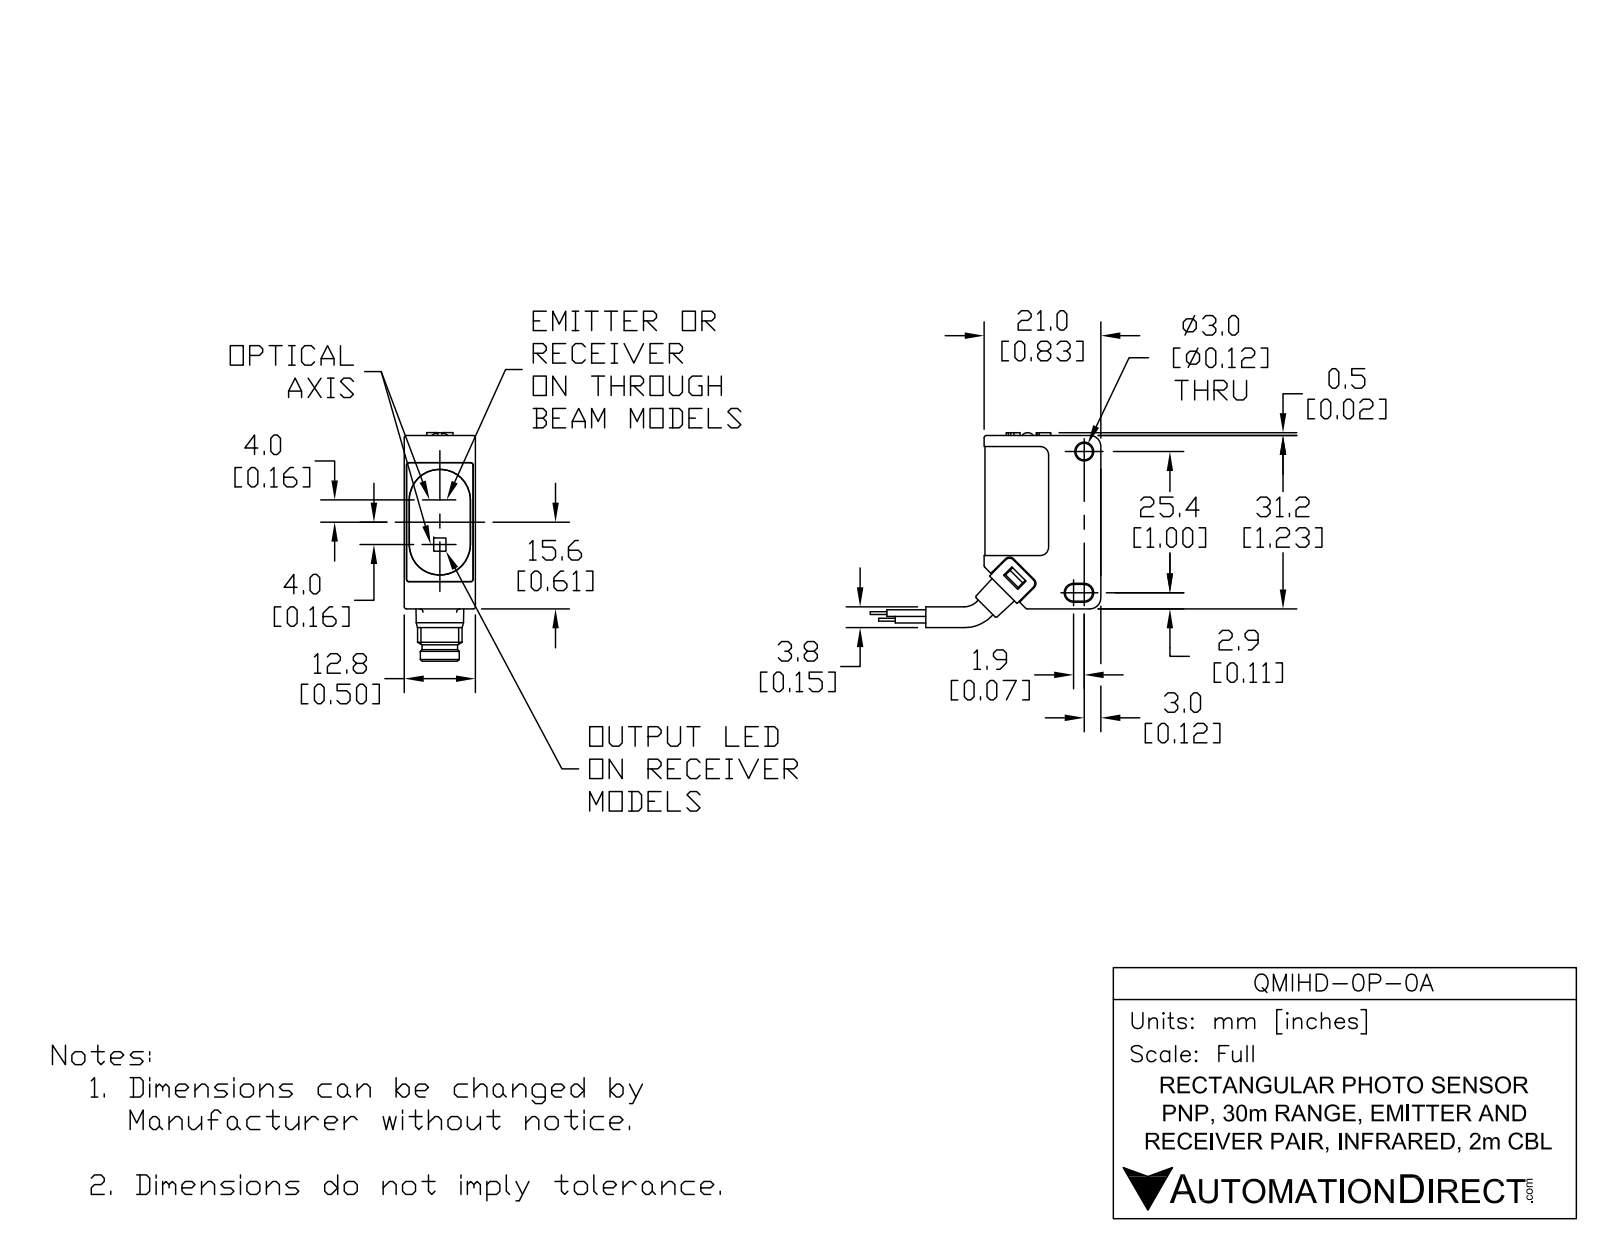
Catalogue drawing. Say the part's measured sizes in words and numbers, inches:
The part is named "QMIHD-0P-0A". Its 3-D file was written by "SolidWorks 2017 (AUTOMOTIVE_DESIGN)". It is 8 solids with 236 faces: 123 planar, 89 cylindrical and 24 other. Overall it measures 3.181 by 1.02 by 0.512 inches. Its volume is 0.47 cubic inches and its surface area 8.336 square inches. Round holes: 2 of diameter 0.118, 1 of diameter 0.148, 1 of diameter 0.224, 1 of diameter 0.283. Round bosses or shafts: 1 of diameter 0.138. Partial cylindrical surfaces (rounded edges, fillets, slot ends): 13 of radius 0.016, 8 of radius 0.039, 6 of radius 0.02, 6 of radius 0.059, 4 of radius 0.024, 2 of radius 0.035, 2 of radius 0.065, 2 of radius 0.079. The main face-to-face distances are 0.02, 0.498, 0.016, 0.504, 0.059, 0.138, 0.488, 0.079, 0.482, 0.492.
